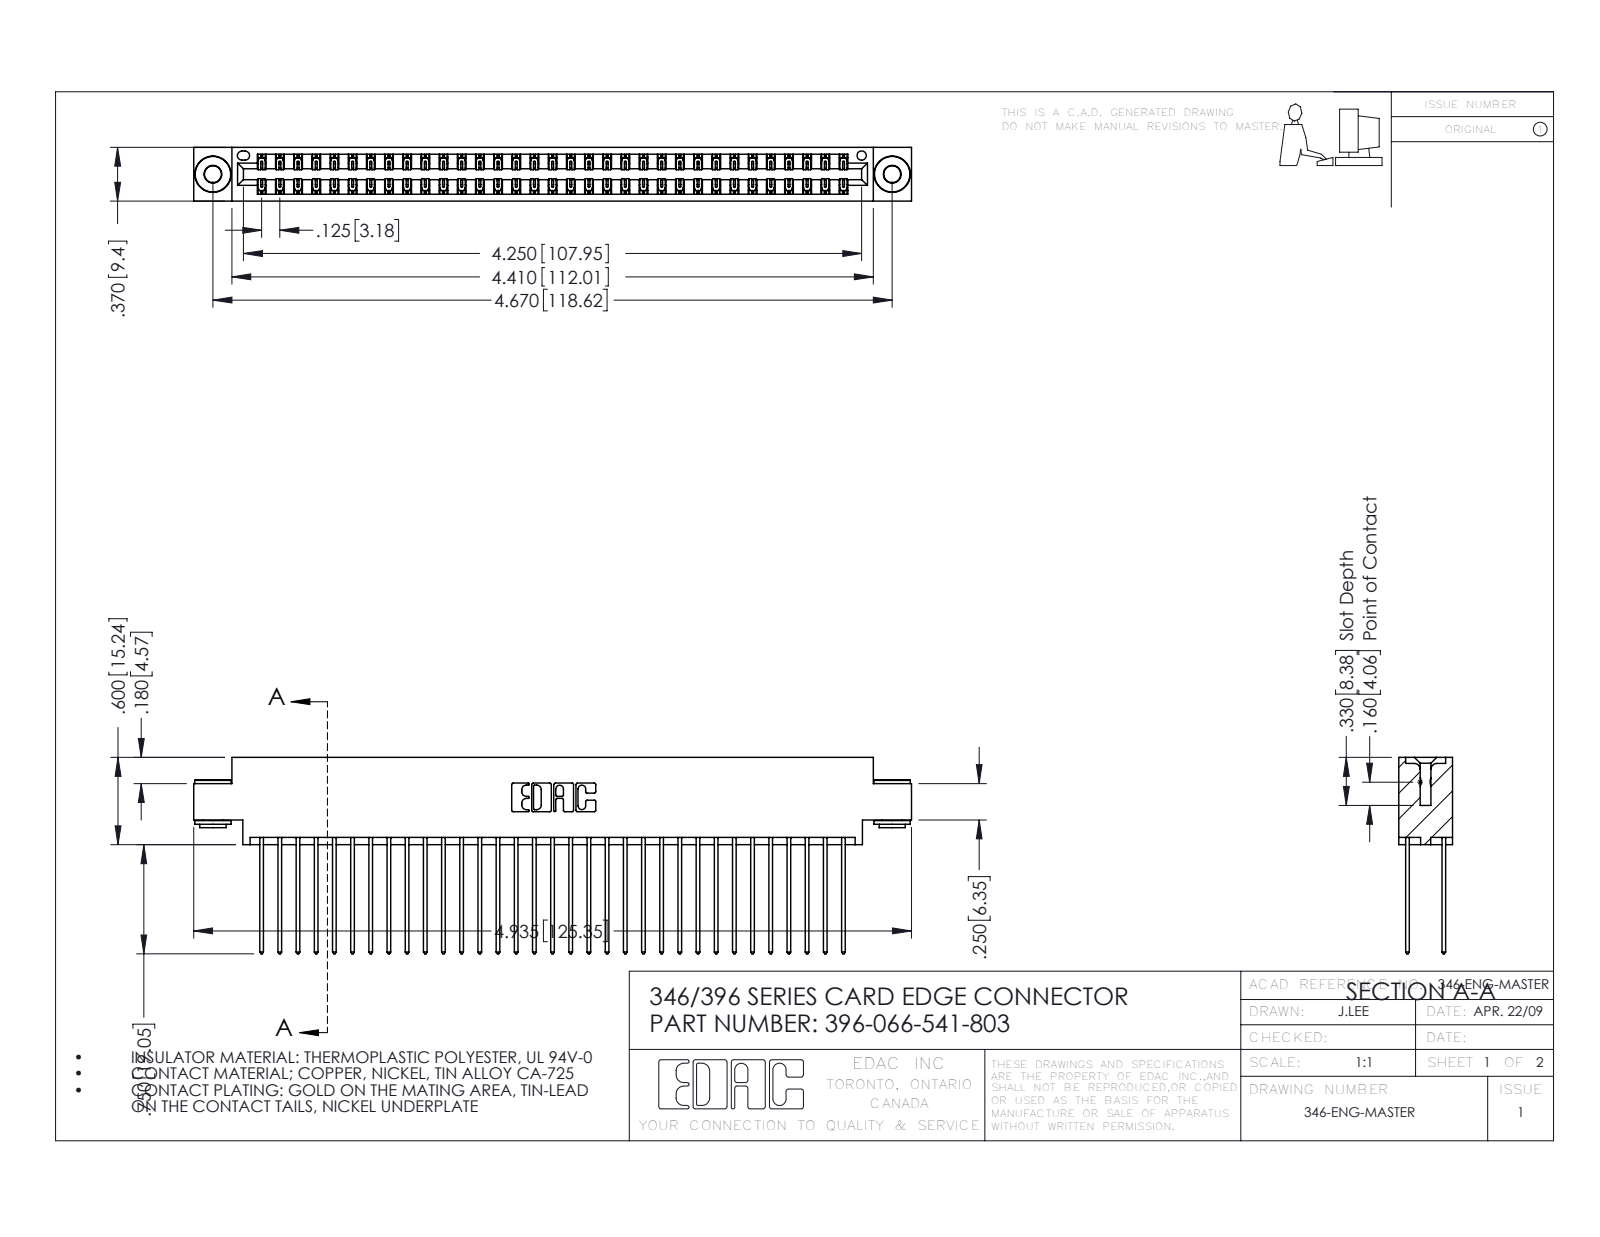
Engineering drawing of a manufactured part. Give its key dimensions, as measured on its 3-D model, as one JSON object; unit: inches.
{"part_name": "346 Part_0.170 Offset - 0.156 Dia-TH; 345-250-002_345-250-002-102; 396-066-541-803; 345-292-001_345-293-141", "step_written_by": "SolidWorks 2016 (CONFIG_CONTROL_DESIGN)", "units": "inches", "bodies": {"solids": 69, "faces": 3596, "planar": 2400, "cylindrical": 1188, "other": 8}, "overall_size": [4.935, 1.35, 0.37], "volume_in3": 0.756, "surface_area_in2": 29.62, "round_holes": [[0.116, 2], [0.156, 2], [0.064, 1]], "round_bosses_or_shafts": [[0.25, 2], [0.18, 2], [0.136, 2]], "partial_cylinders_radius": [[0.006, 99], [0.01, 66], [0.01, 22], [0.007, 6], [0.031, 6], [0.026, 3], [0.014, 2], [0.022, 2]], "face_to_face_distances": [0.048, 0.322, 0.25, 0.025, 0.072, 0.298, 0.37, 0.275, 0.225, 0.148], "hole_center_spacings": [0.246, 4.462, 4.67]}
